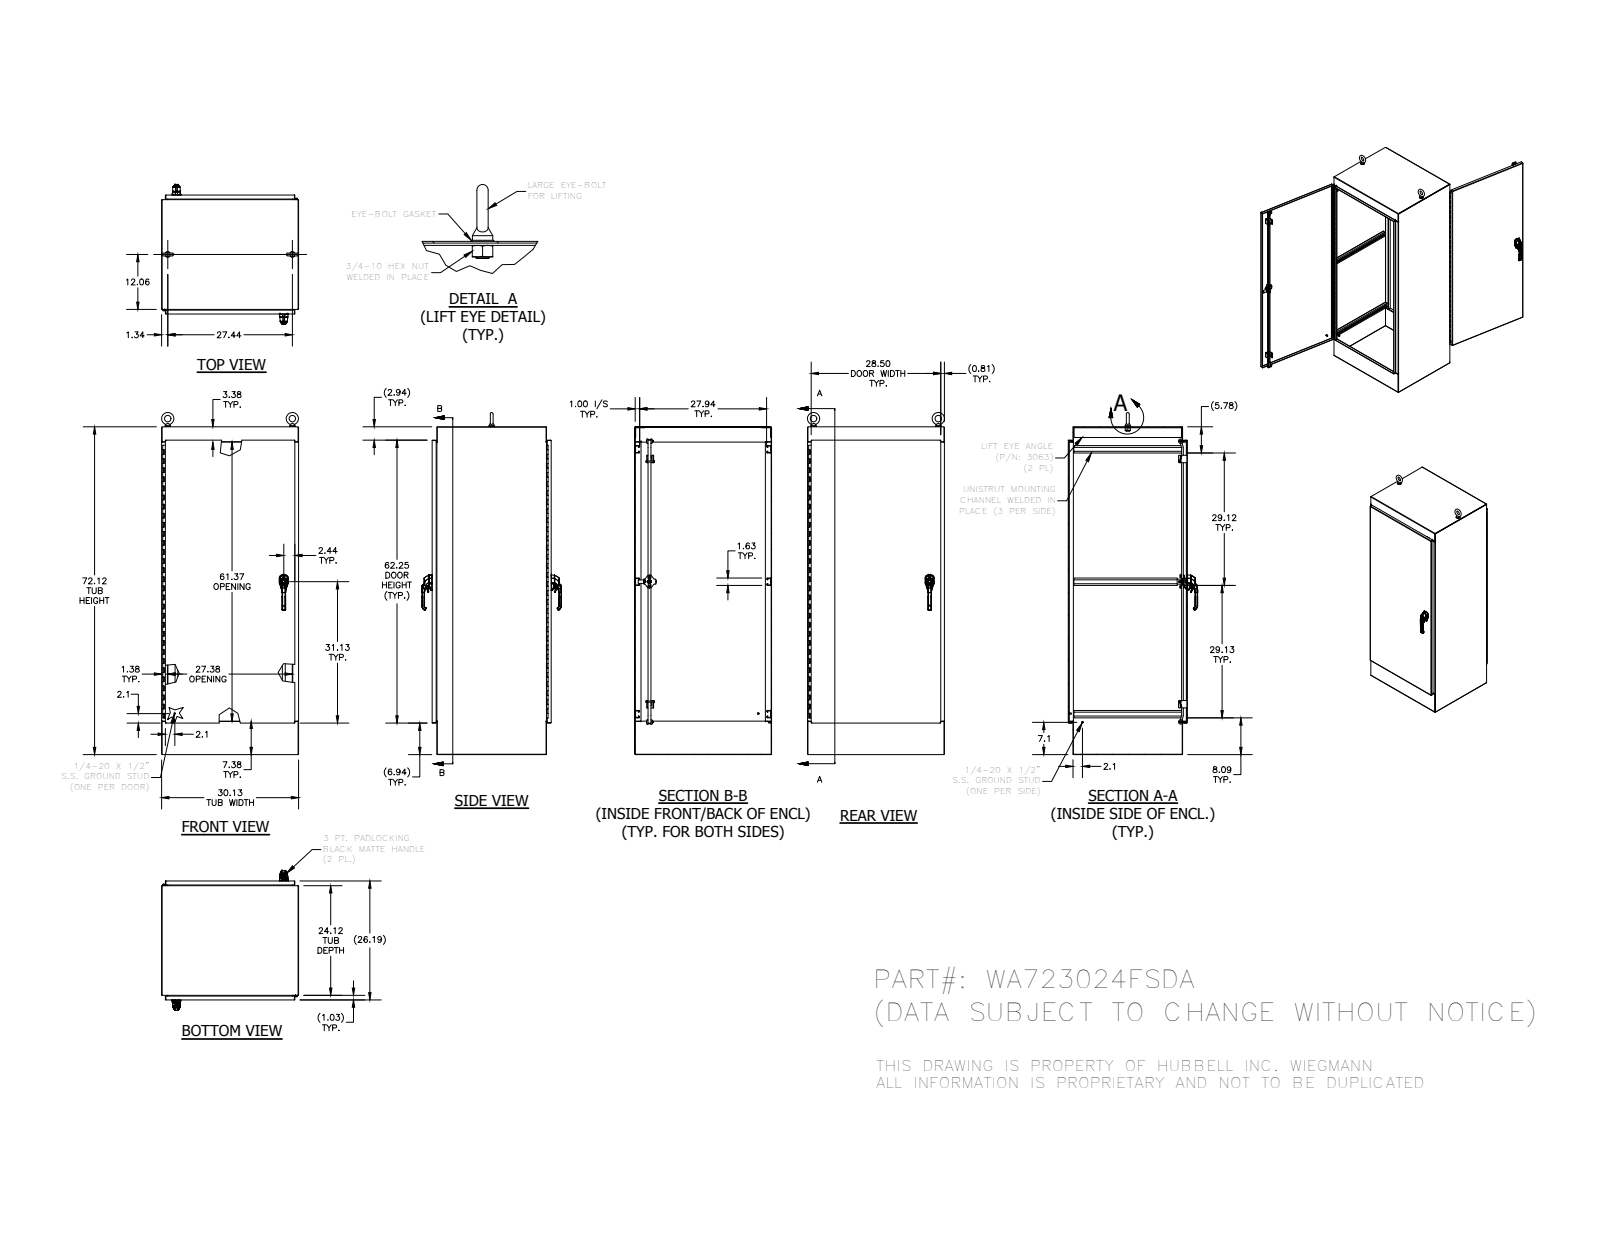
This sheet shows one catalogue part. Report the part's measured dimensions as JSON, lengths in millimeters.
{"part_name": "WA7224FSDALRS; WA3024FSDABTM; WA3024FSDATOP; WA7230FSDADR (+8 more)", "step_written_by": "Autodesk Inventor 2014 (AUTOMOTIVE_DESIGN)", "units": "millimeters", "bodies": {"solids": 84, "faces": 5638, "planar": 2368, "cylindrical": 2004, "other": 1266}, "overall_size": [1911.29, 780.41, 765.17], "volume_mm3": 17360000, "surface_area_mm2": 14840000, "round_holes": [[7.02, 16], [5.08, 8], [5.4, 6], [6, 6], [7.11, 6], [6.13, 4], [6.35, 4], [6.41, 4], [10.16, 4], [10.33, 4], [10.5, 4], [11.43, 4]], "round_bosses_or_shafts": [[6.35, 6], [25.4, 4], [14.29, 4], [13.37, 4], [12.7, 4], [9.52, 4], [8.56, 4], [7.94, 4]], "partial_cylinders_radius": [[0.5, 333], [0.3, 170], [0.47, 38], [0.25, 32], [2, 30], [1.27, 28], [0.79, 26], [3, 24]], "face_to_face_distances": [2.38, 662.79, 762.8, 760.42, 660.41, 665.17, 765.18, 1829.59, 26.3, 26.09], "hole_center_spacings": [600.04, 9.66, 9.7, 9.71, 12.5, 19.36, 19.4, 22.5]}
